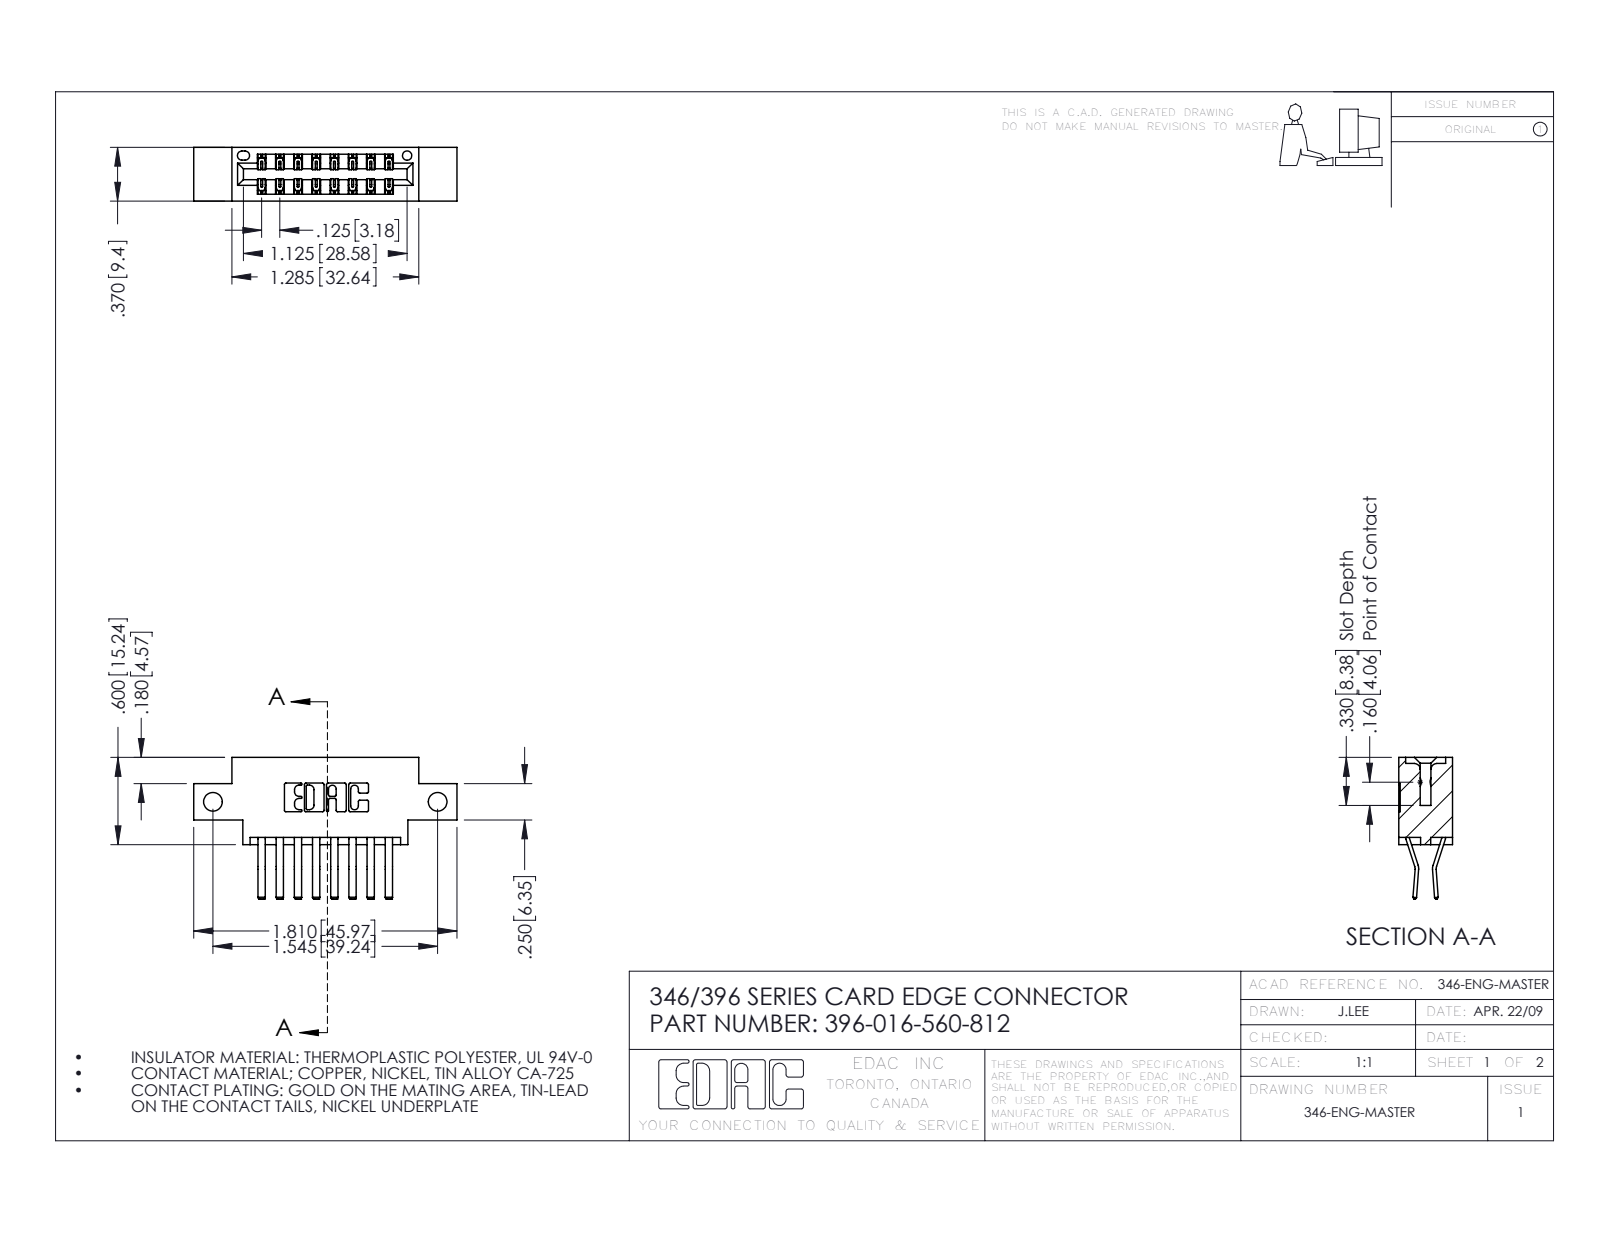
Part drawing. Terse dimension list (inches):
name: 396-016-560-812; 345-292-001_560 Tail; 346 Part_0.170 Offset - Side Mount
written by: SolidWorks 2016 (CONFIG_CONTROL_DESIGN)
unit: in
bodies: 17 solids, 990 faces (640 planar, 350 cylindrical, 0 other)
size: 1.81 × 0.975 × 0.37
volume: 0.249 in³; area: 8.368 in²
holes: 2× ⌀0.128, 1× ⌀0.064
rounds: 24× R0.006, 22× R0.01, 6× R0.007, 6× R0.031, 3× R0.026, 2× R0.01, 2× R0.014, 2× R0.022
face distances: 0.25, 0.37, 0.048, 0.322, 0.025, 0.148, 0.222, 0.1, 0.174, 0.072
hole spacings: 1.545
